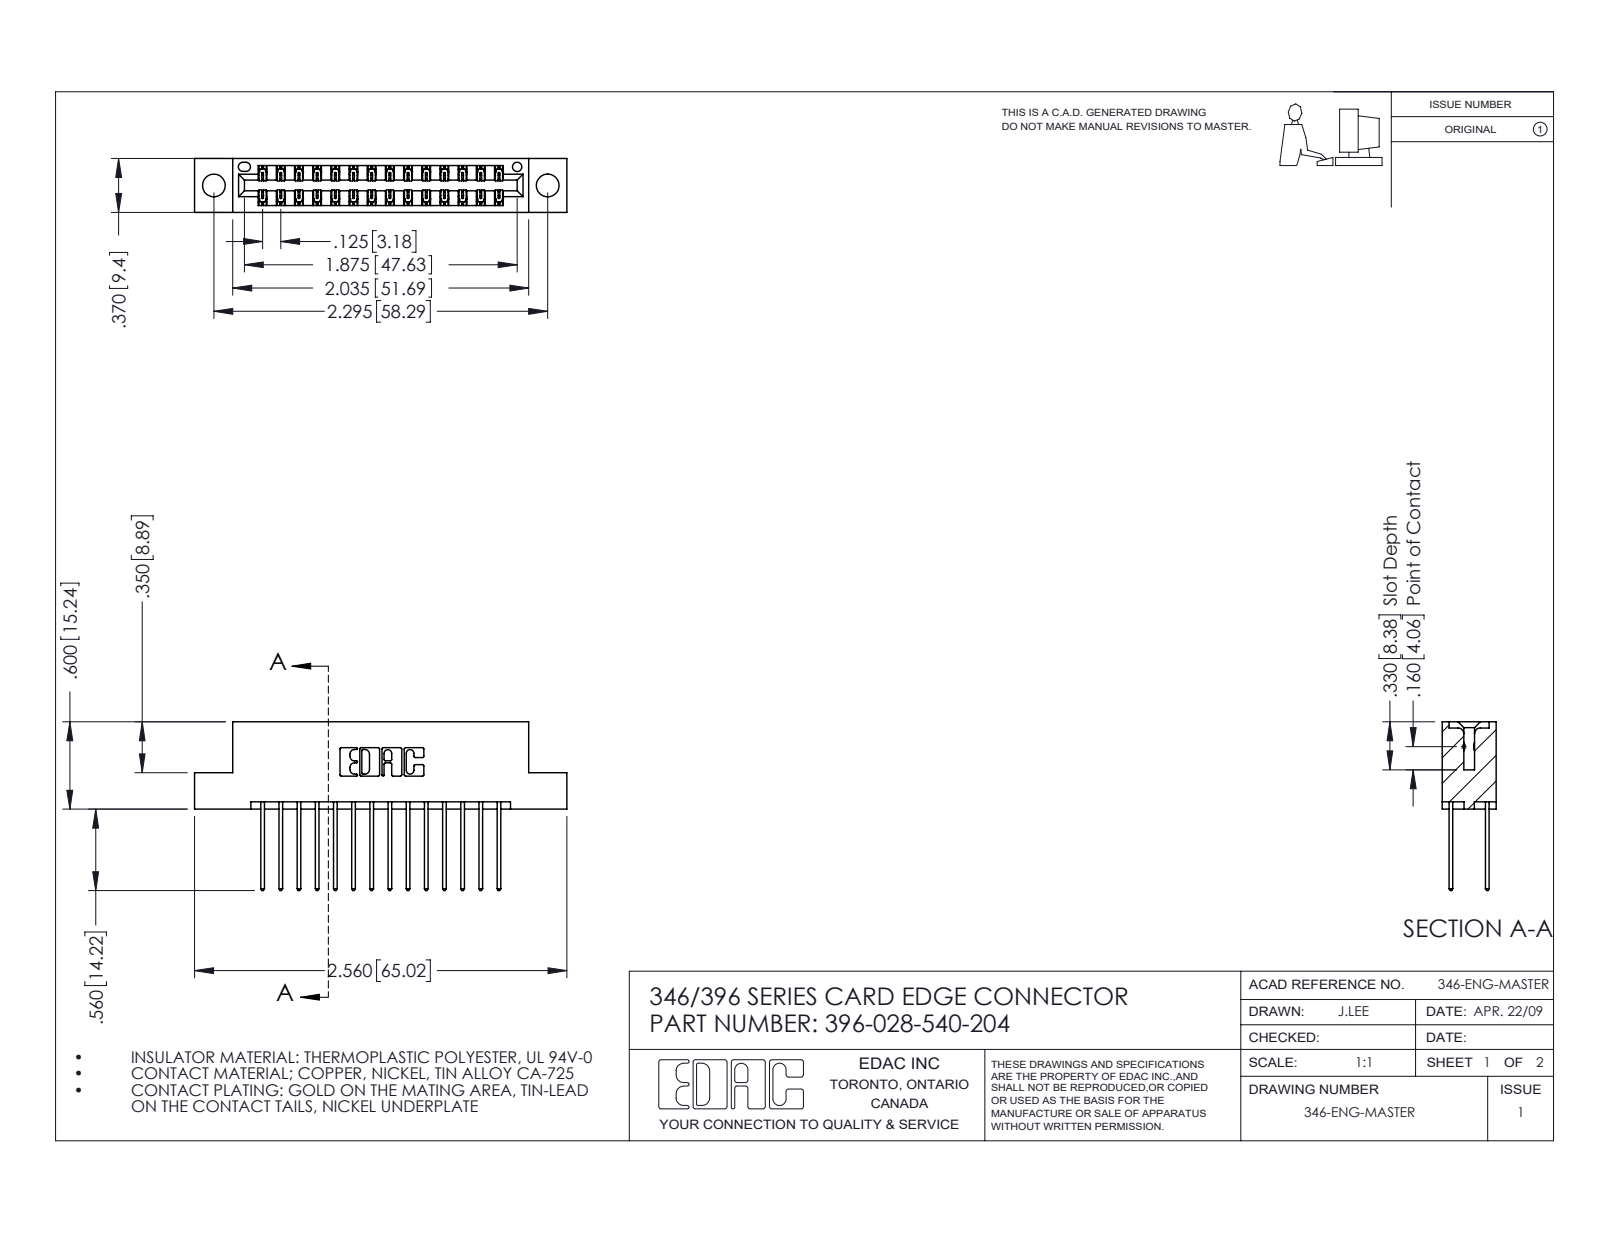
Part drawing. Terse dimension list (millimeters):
name: 345-292-001_345-293-140; 346 Part_Flush Mounting Lugs - 0.156 Dia-TH; 396-028-540-204
written by: SolidWorks 2016 (CONFIG_CONTROL_DESIGN)
unit: mm
bodies: 29 solids, 1578 faces (1056 planar, 522 cylindrical, 0 other)
size: 65 × 29.5 × 9.4
volume: 6 150 mm³; area: 8 316 mm²
holes: 2× ⌀4, 1× ⌀1.6
rounds: 42× R0.2, 28× R0.3, 22× R0.3, 6× R0.2, 6× R0.8, 3× R0.7, 2× R0.4, 2× R0.6
face distances: 1.2, 8.2, 6.4, 9.4, 1.8, 7.6, 0.6, 7, 3.8, 5.6
hole spacings: 6.2, 53.1, 58.3
